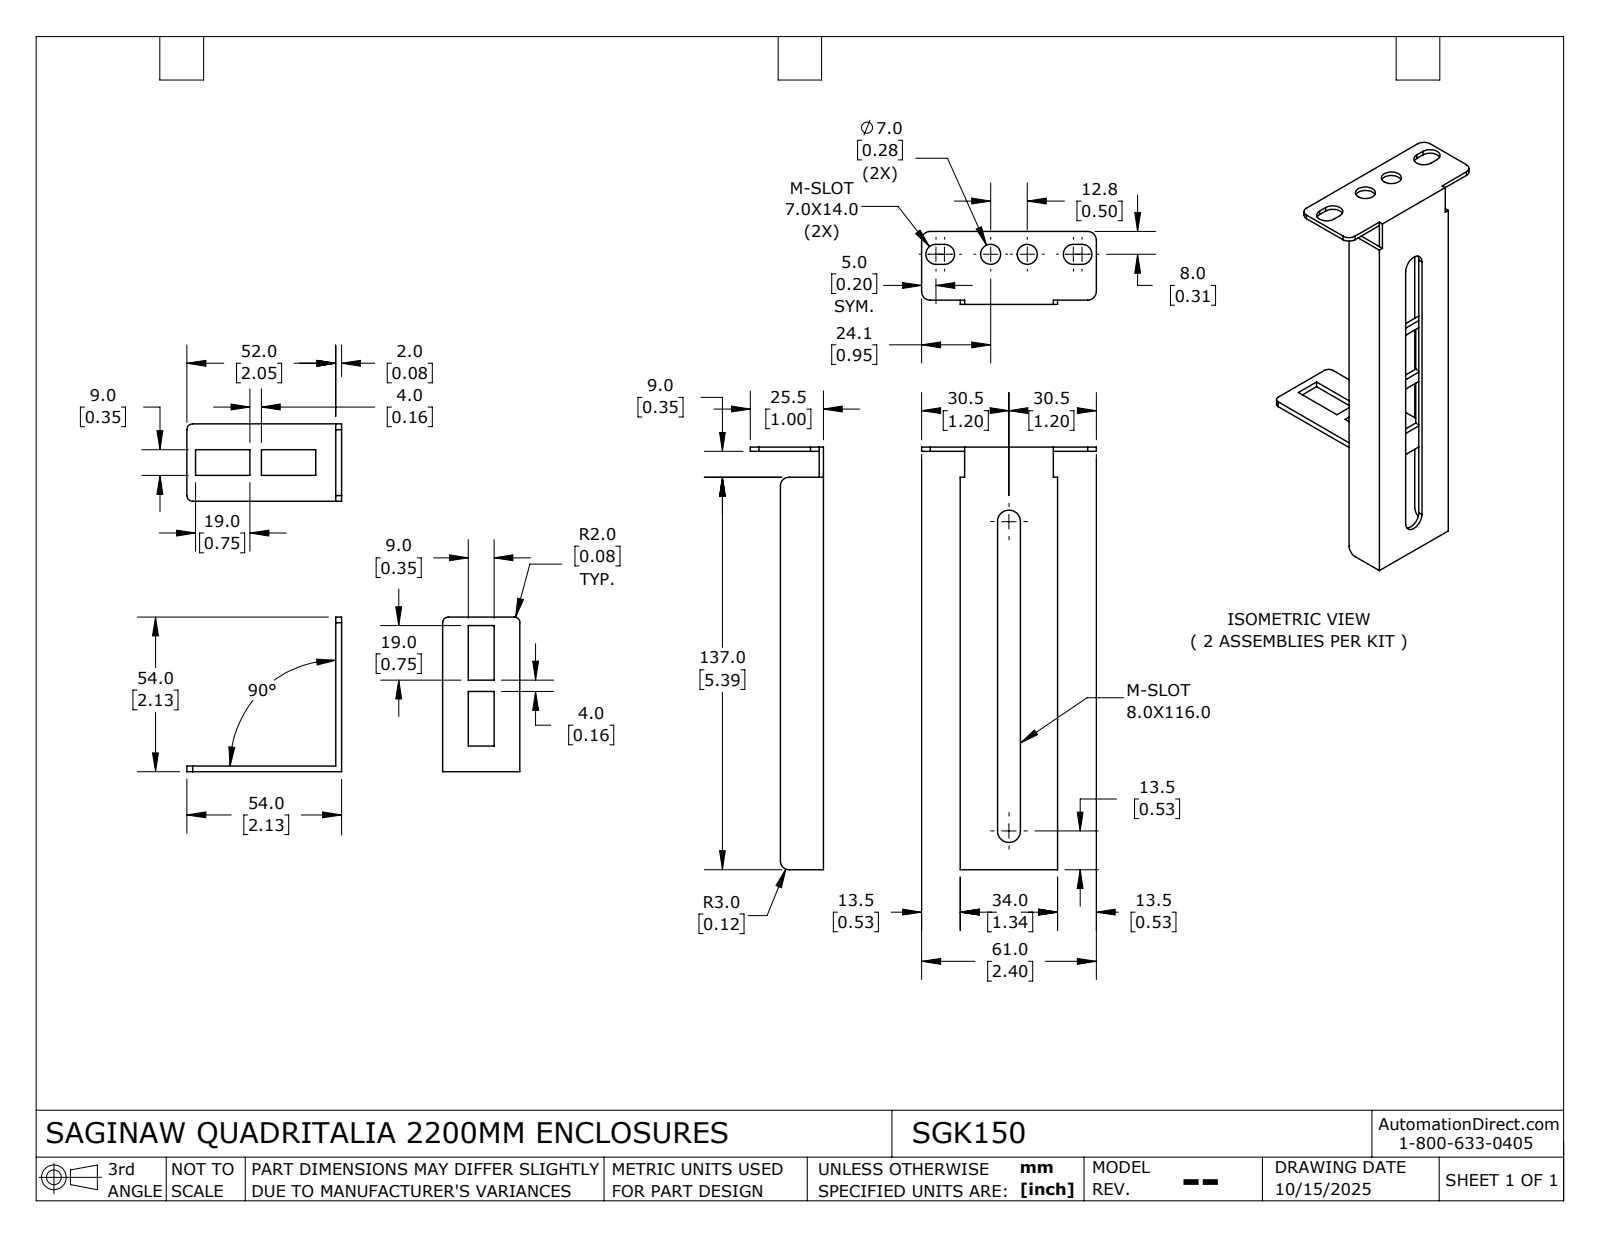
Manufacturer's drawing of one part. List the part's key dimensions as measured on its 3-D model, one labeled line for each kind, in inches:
Part name (STEP PRODUCT): SGK150
STEP written by: SolidWorks 2024 (AUTOMOTIVE_DESIGN)
Units: inches
Bodies: 4 solids, 140 faces (100 planar, 40 cylindrical, 0 other)
Overall size (bounding box): 8.64 × 5.807 × 2.402
Volume: 2.182 in³ · Surface area: 76.41 in²
Round holes (diameter × count): ⌀0.276 ×4
Partial cylindrical surfaces — rounded edges, fillets, slot ends (radius × count): R0.118 ×12, R0.138 ×8, R0.079 ×6, R0.157 ×2
Main face-to-face distances: 0.059, 8.581, 1.28, 0.079, 8.522, 1.339, 8.64, 1.22, 0.138, 4.109
Hole centre spacings: 0.504, 7.262, 7.28
